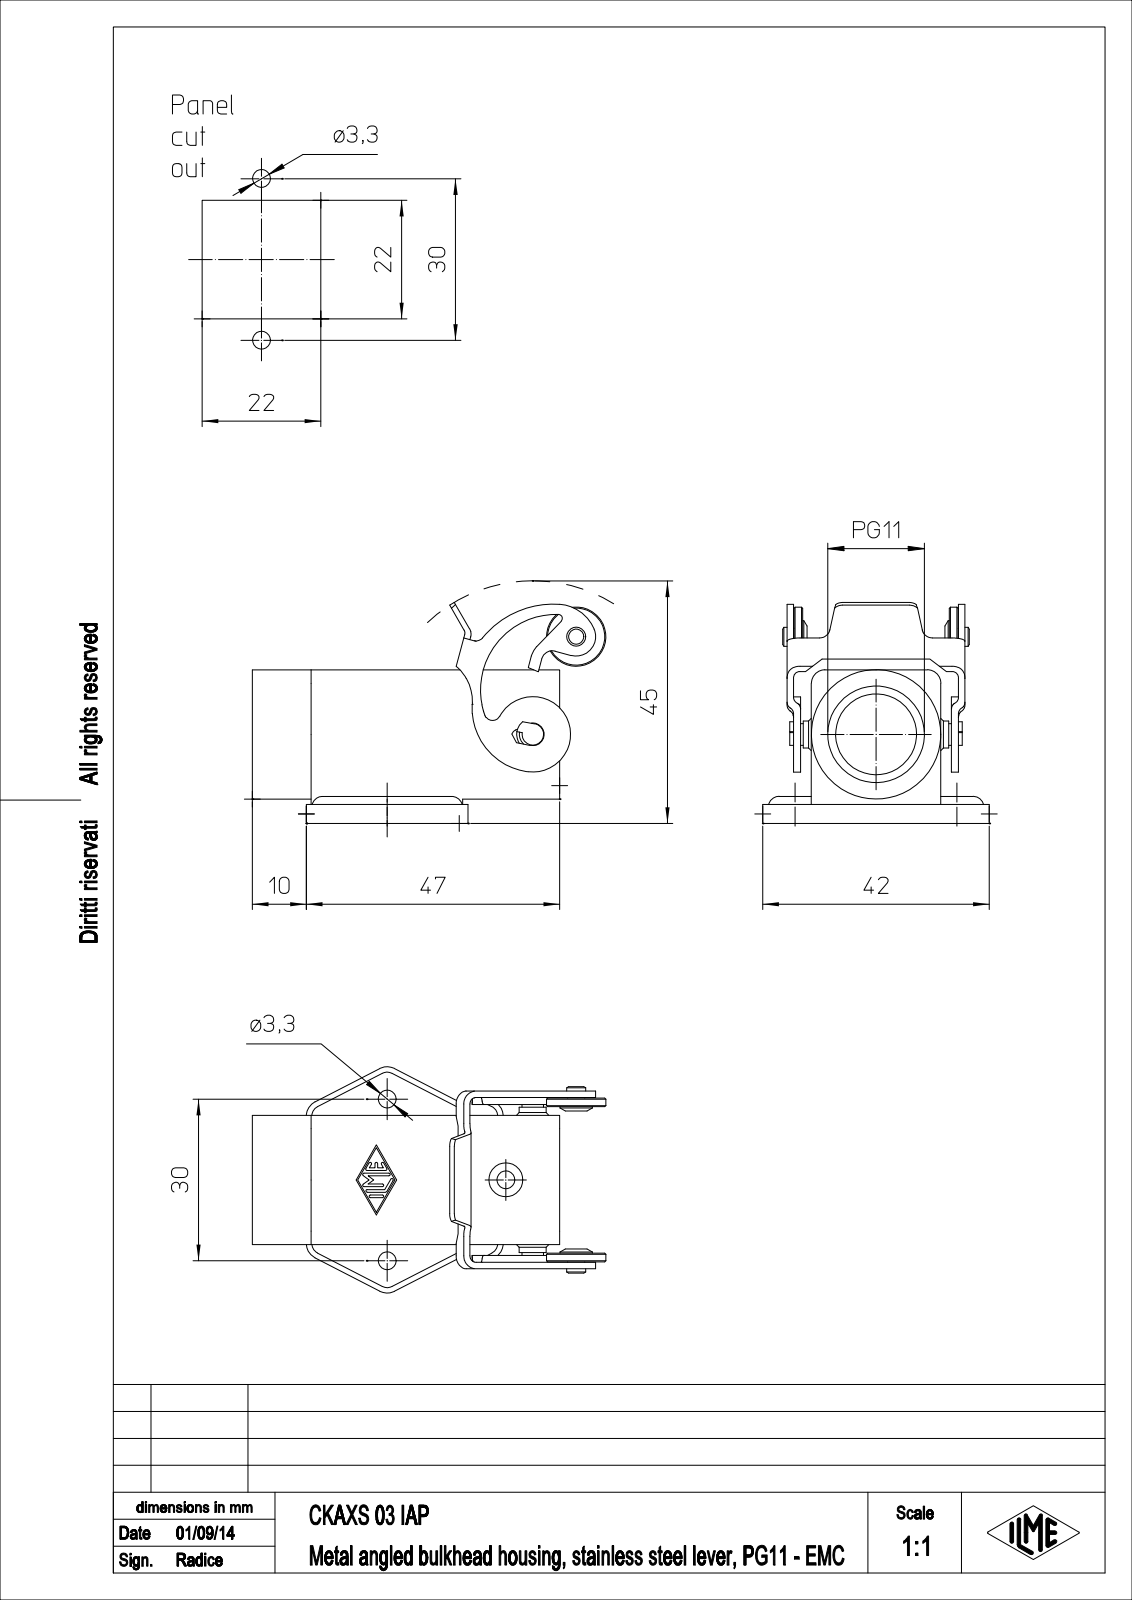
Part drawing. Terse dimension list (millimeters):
name: CKAXS 03 IAP
written by: Autodesk Inventor 7 (AUTOMOTIVE_DESIGN)
unit: mm
bodies: 1 solid, 339 faces (132 planar, 146 cylindrical, 61 other)
size: 60.57 × 42 × 41.02
volume: 11 818 mm³; area: 13 426 mm²
holes: 3× ⌀3.3, 2× ⌀3.4, 1× ⌀15, 1× ⌀17.93
bosses: 1× ⌀24, 1× ⌀11, 1× ⌀6, 1× ⌀5, 1× ⌀4, 1× ⌀3.5, 1× ⌀3.2
rounds: 15× R2, 14× R0.25, 8× R1.2, 8× R1.75, 7× R2.5, 7× R3, 4× R1.25, 2× R1.5
face distances: 1.25, 22.75, 21.5, 24, 28.5, 27.25, 5.75, 2, 4.5, 3.25
hole spacings: 21.57, 30
